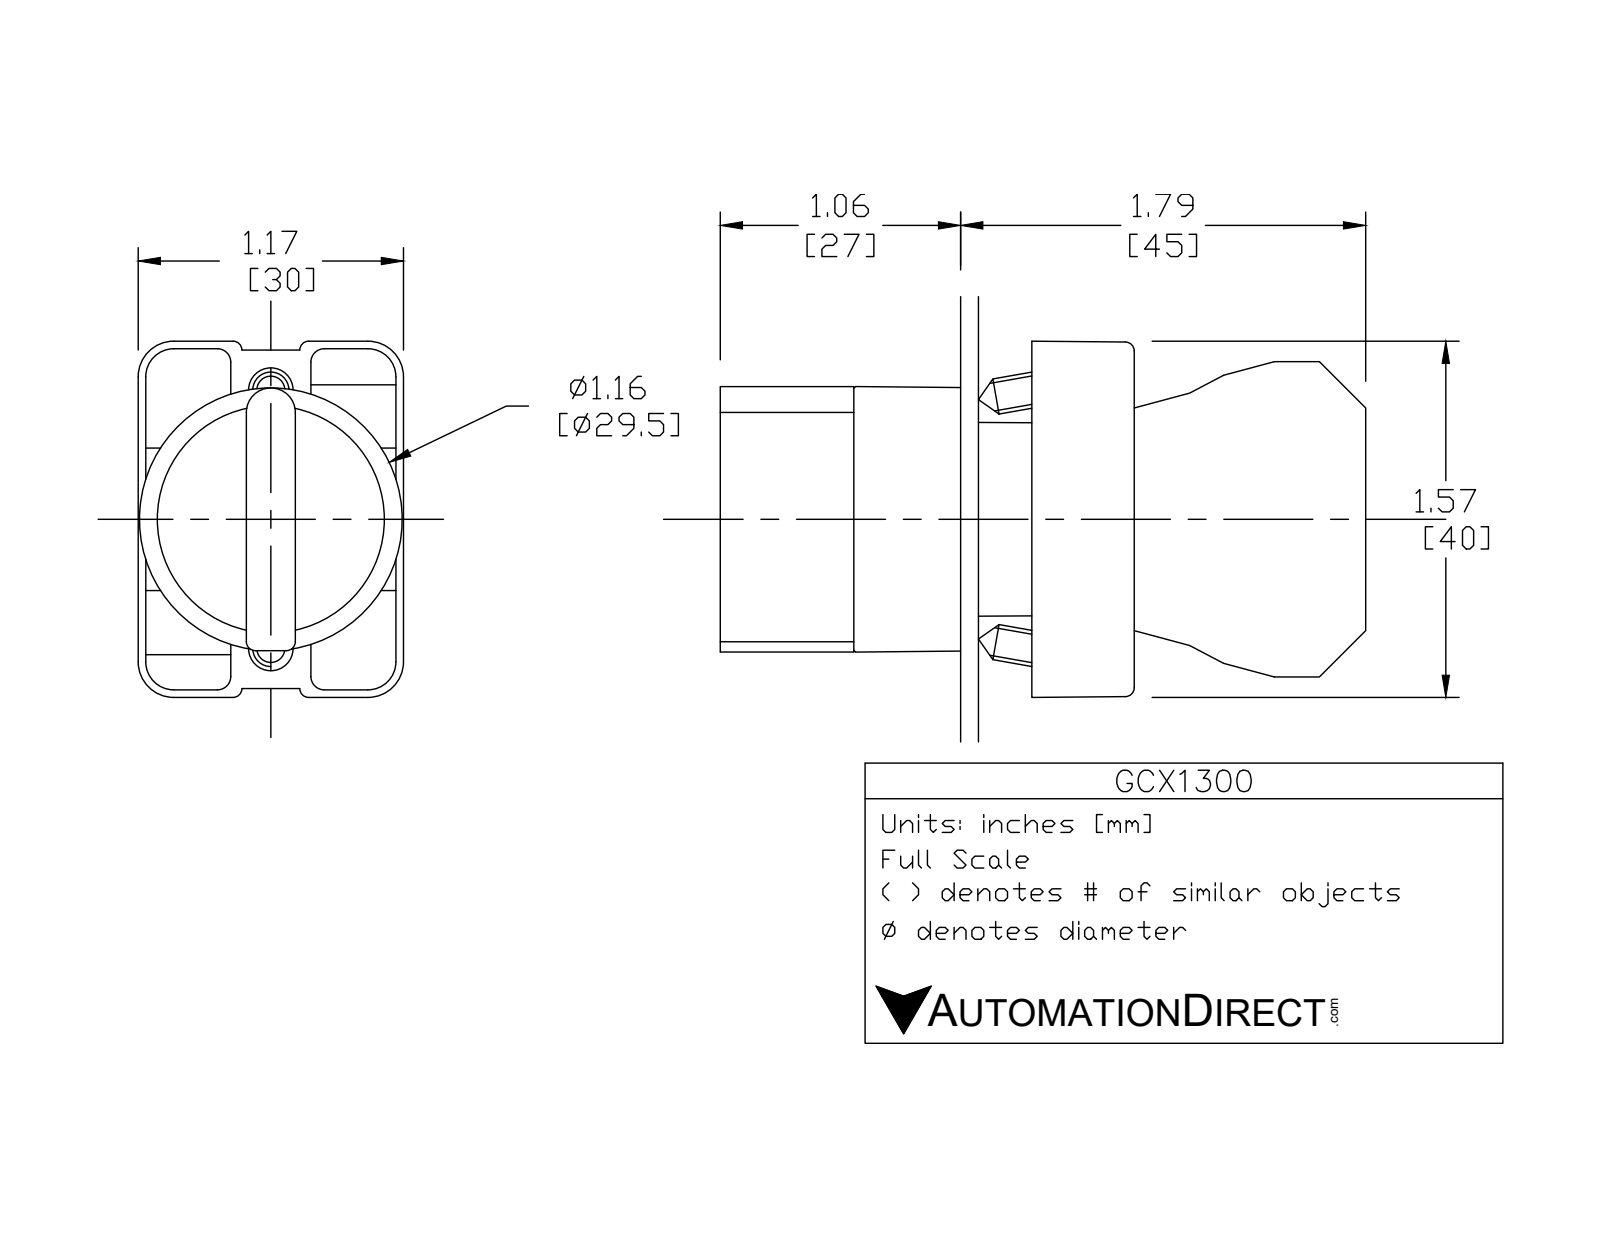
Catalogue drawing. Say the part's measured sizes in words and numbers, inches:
The part is named "ecx1029; GCX1300; ecx1040; GCX1300 OPERATOR". Its 3-D file was written by "SolidWorks 2016 (AUTOMOTIVE_DESIGN)". It is 6 solids with 396 faces: 232 planar, 137 cylindrical and 27 other. Overall it measures 2.78 by 1.581 by 1.177 inches. Its volume is 1.88 cubic inches and its surface area 28.65 square inches. Round holes: 2 of diameter 0.079, 2 of diameter 0.124, 2 of diameter 0.13, 1 of diameter 0.087, 1 of diameter 0.197, 1 of diameter 0.878, 1 of diameter 0.888, 1 of diameter 1.024. Round bosses or shafts: 2 of diameter 0.157, 1 of diameter 1.175, 1 of diameter 1.004, 1 of diameter 0.945, 1 of diameter 0.856, 1 of diameter 0.78. Partial cylindrical surfaces (rounded edges, fillets, slot ends): 24 of radius 0.059, 12 of radius 0.041, 12 of radius 0.124, 12 of radius 0.157, 6 of radius 0.039, 2 of radius 0.128, 1 of radius 0.02, 1 of radius 0.063. The main face-to-face distances are 0.72, 0.579, 0.033, 0.472, 0.031, 0.474, 0.703, 0.689, 1.193, 0.598. The hole center spacings are 0.236, 0.544, 0.472, 0.49.
